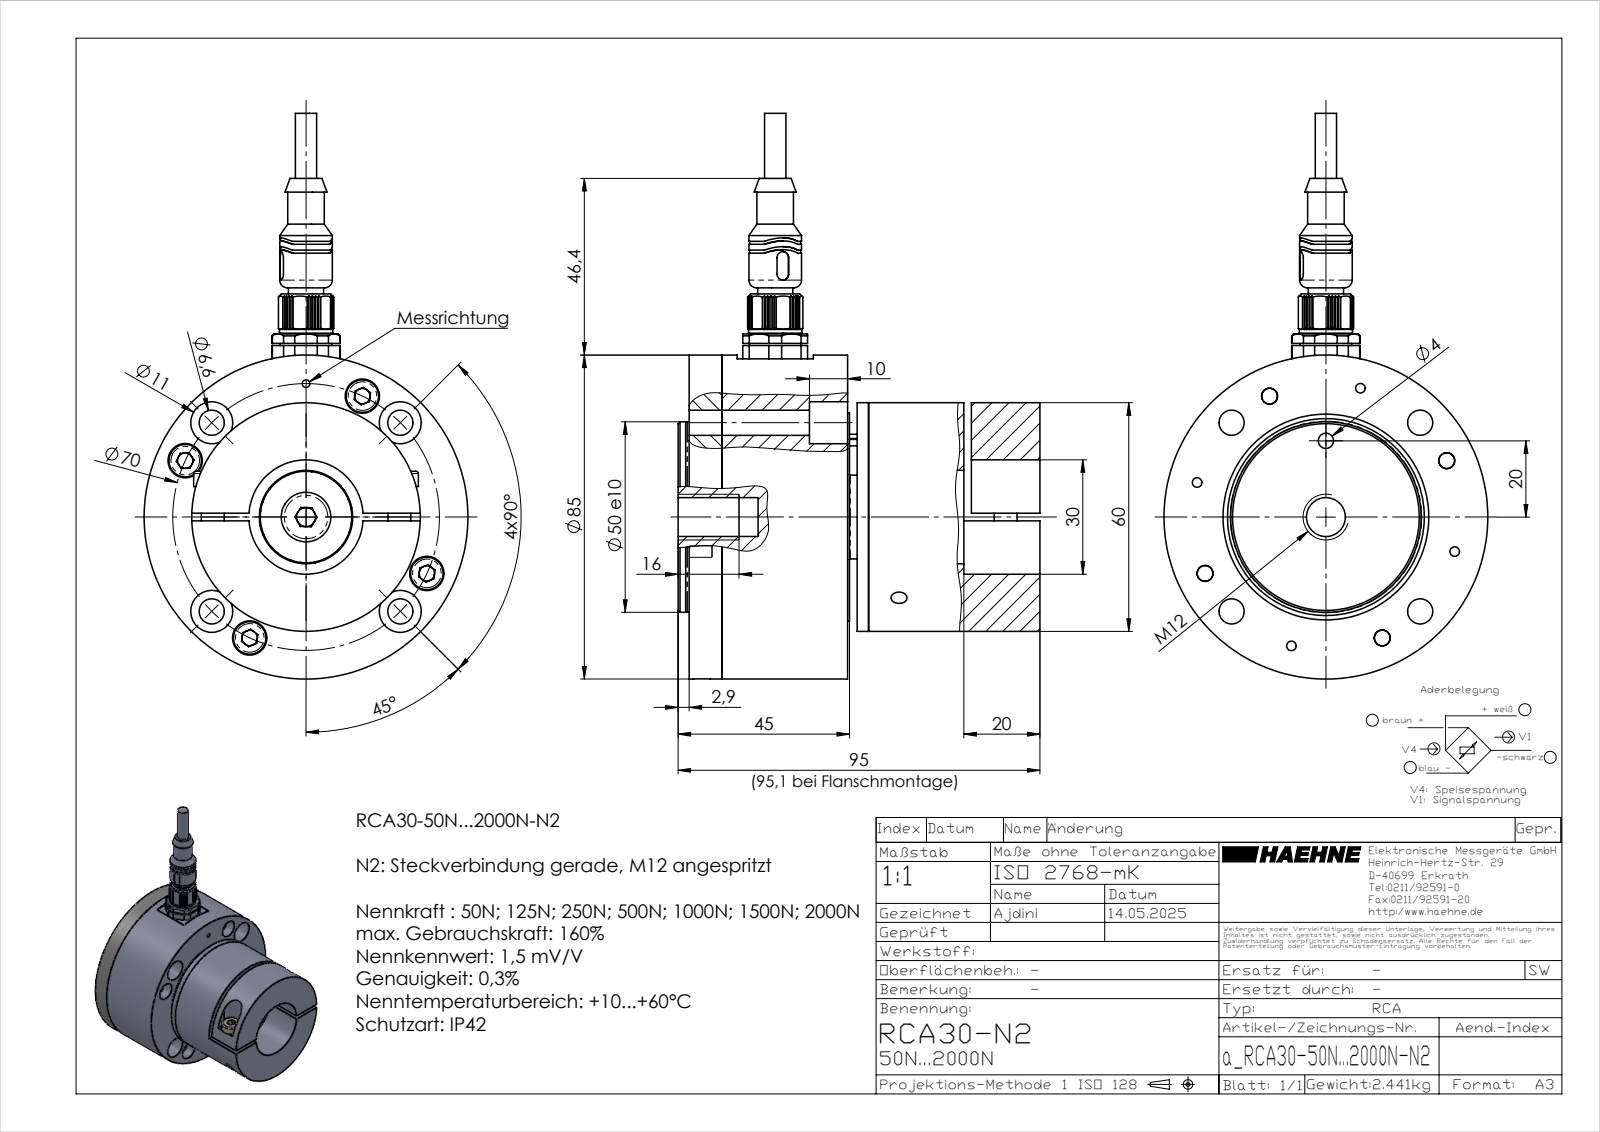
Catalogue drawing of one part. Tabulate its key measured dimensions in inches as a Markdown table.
| quantity | value |
| --- | --- |
| part name | inafag_1203-tvh_7zkvytp7yxkimpdvw8sj0b5w4_24; inafag_1203-tvh_7zkvytp7yxkimpdvw8sj0b5w4_19; Y02043Z1 inafag_1203-tvh_7zkvytp7yxkimpdvw8sj0b5w4; inafag_1203-tvh_7zkvytp7yxkimpdvw8sj0b5w4_09 (+8 more) |
| STEP written by | SolidWorks 2023 (AUTOMOTIVE_DESIGN) |
| units | inches |
| bodies | 53 solids, 1169 faces (647 planar, 300 cylindrical, 222 other) |
| overall size | 5.844 × 3.744 × 3.346 |
| volume | 22.05 in³ |
| surface area | 174.4 in² |
| round holes (diameter × count) | 0.134 × 9, 0.098 × 8, 0.26 × 6, 0.165 × 5, 0.433 × 5, 0.043 × 4, 0.045 × 4, 0.063 × 4, 0.073 × 4, 0.157 × 4, 0.209 × 4, 0.354 × 4 |
| round bosses / shafts (diameter × count) | 0.118 × 9, 0.224 × 8, 0.335 × 4, 0.197 × 4, 0.071 × 4, 0.061 × 4, 0.059 × 4, 0.039 × 4 |
| partial cylindrical surfaces (radius × count) | 0.008 × 16, 0.012 × 9, 0.016 × 4, 0.021 × 4, 0.039 × 4, 0.05 × 4, 0.472 × 4, 0.063 × 2 |
| main face-to-face distances | 0.118, 0.079, 0.339, 1.854, 0.457, 1.772, 1.969, 1.181, 1.398, 1.972 |
| hole center spacings | 1.378, 1.949, 0.976, 0.992, 1.291, 2.013, 2.223, 0.098 |
